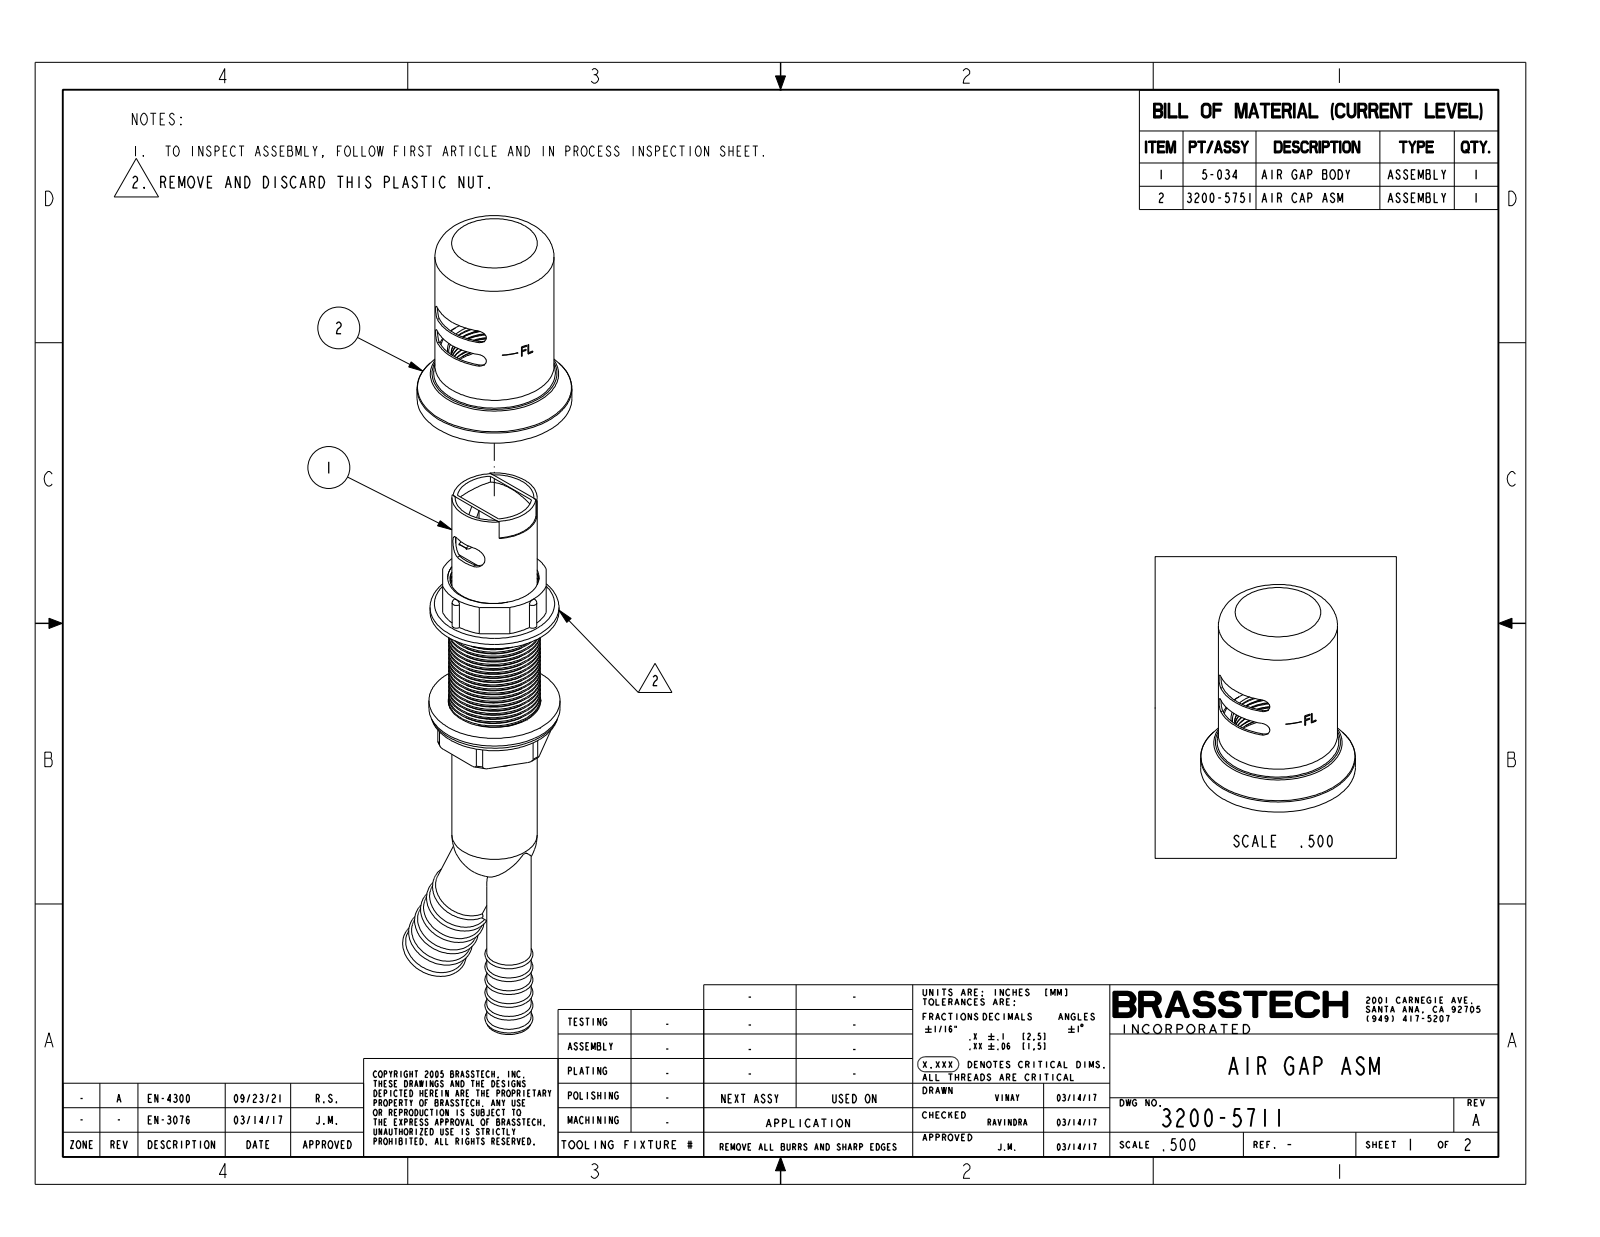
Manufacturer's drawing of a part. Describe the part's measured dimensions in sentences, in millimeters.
The part is named "3200-5711". Its 3-D file was written by "CREO PARAMETRIC BY PTC INC, 2018400 (AUTOMOTIVE_DESIGN)". It is 2 solids with 273 faces: 66 planar, 128 cylindrical and 79 other. Overall it measures 223.6 by 67.2 by 54 millimeters. Its volume is 167 800 cubic millimeters and its surface area 51 620 square millimeters. Round holes: 1 of diameter 30.5, 1 of diameter 32.3, 1 of diameter 32.5, 1 of diameter 40. Round bosses or shafts: 1 of diameter 54, 1 of diameter 45.7, 1 of diameter 44.7, 1 of diameter 41.5, 1 of diameter 32, 1 of diameter 29.7, 1 of diameter 21.7, 1 of diameter 15.5. Partial cylindrical surfaces (rounded edges, fillets, slot ends): 6 of radius 1, 4 of radius 2.5, 2 of radius 4, 1 of radius 20.5. The main face-to-face distances are 23.4, 34.2, 10.8, 89, 89.8, 65.7, 66.4, 54.9, 55.6, 0.8.
